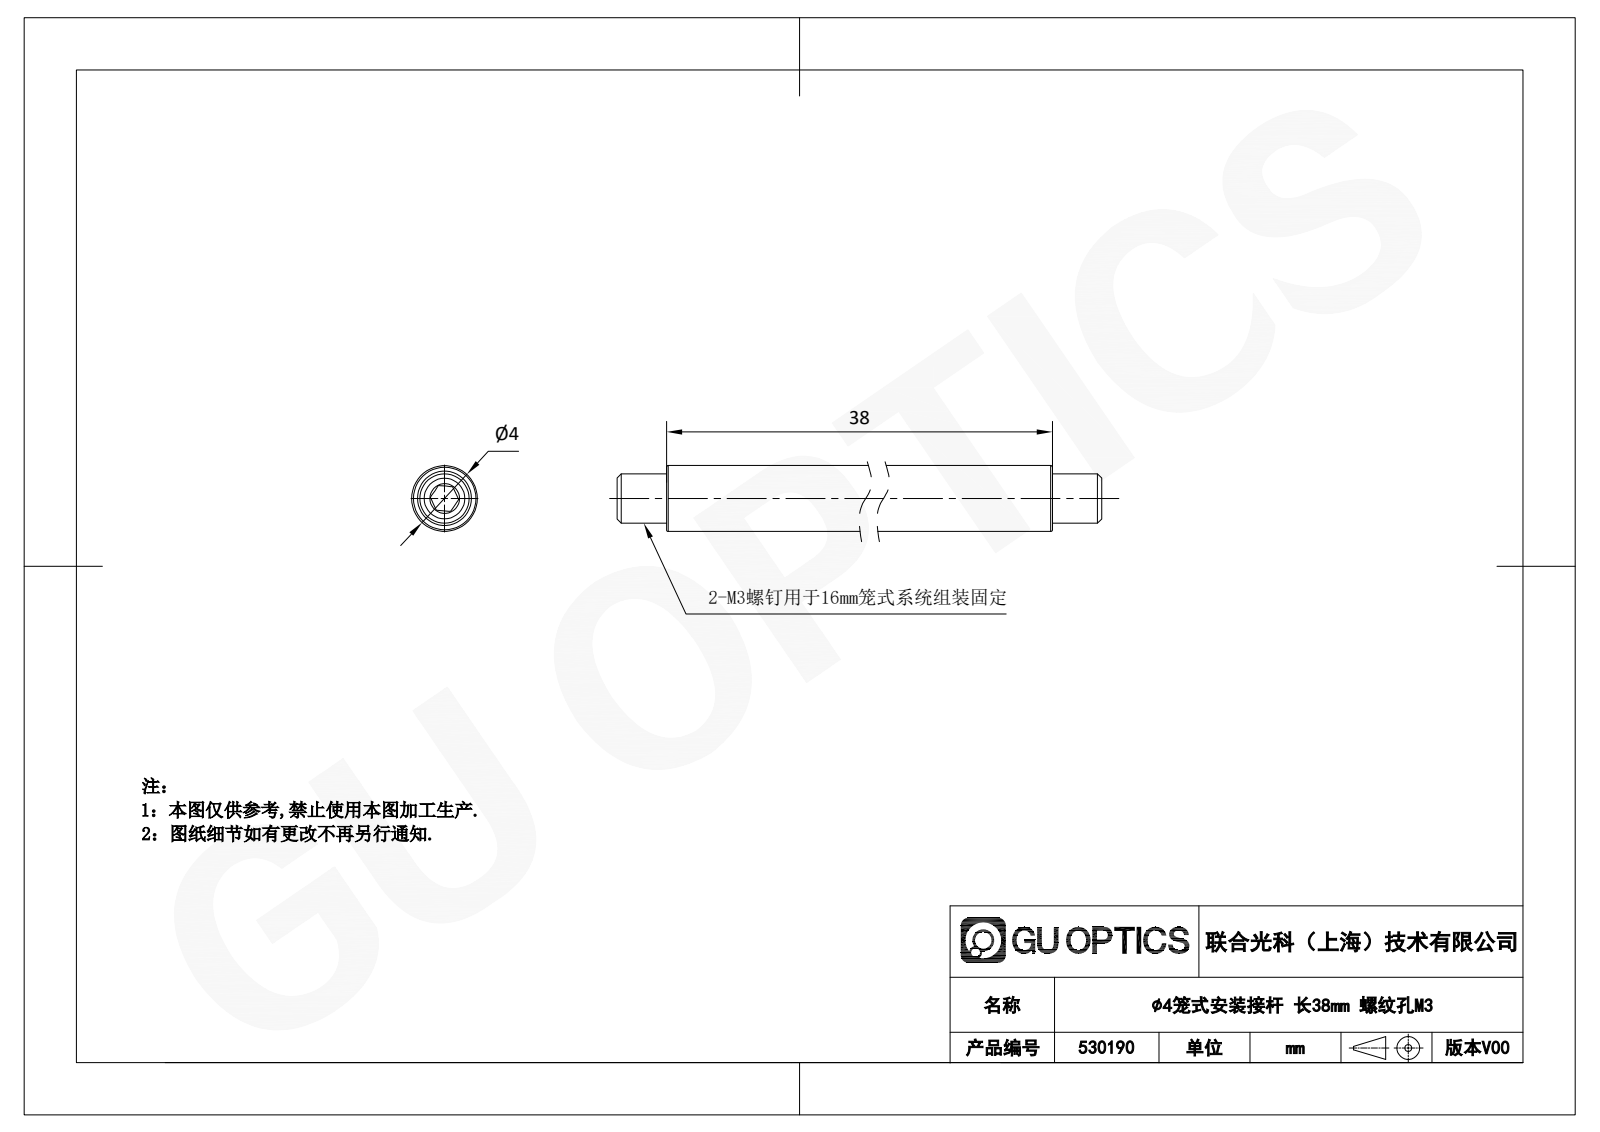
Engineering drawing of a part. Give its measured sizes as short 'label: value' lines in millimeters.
name: 530190
written by: SolidWorks 2020 (CONFIG_CONTROL_DESIGN)
unit: mm
bodies: 3 solids, 37 faces (20 planar, 5 cylindrical, 12 other)
size: 48 × 4 × 4
volume: 527 mm³; area: 767 mm²
holes: 1× ⌀2.5
bosses: 1× ⌀4, 1× ⌀3
face distances: 3, 35, 5, 8, 40, 43, 1.5, 38, 1, 47
